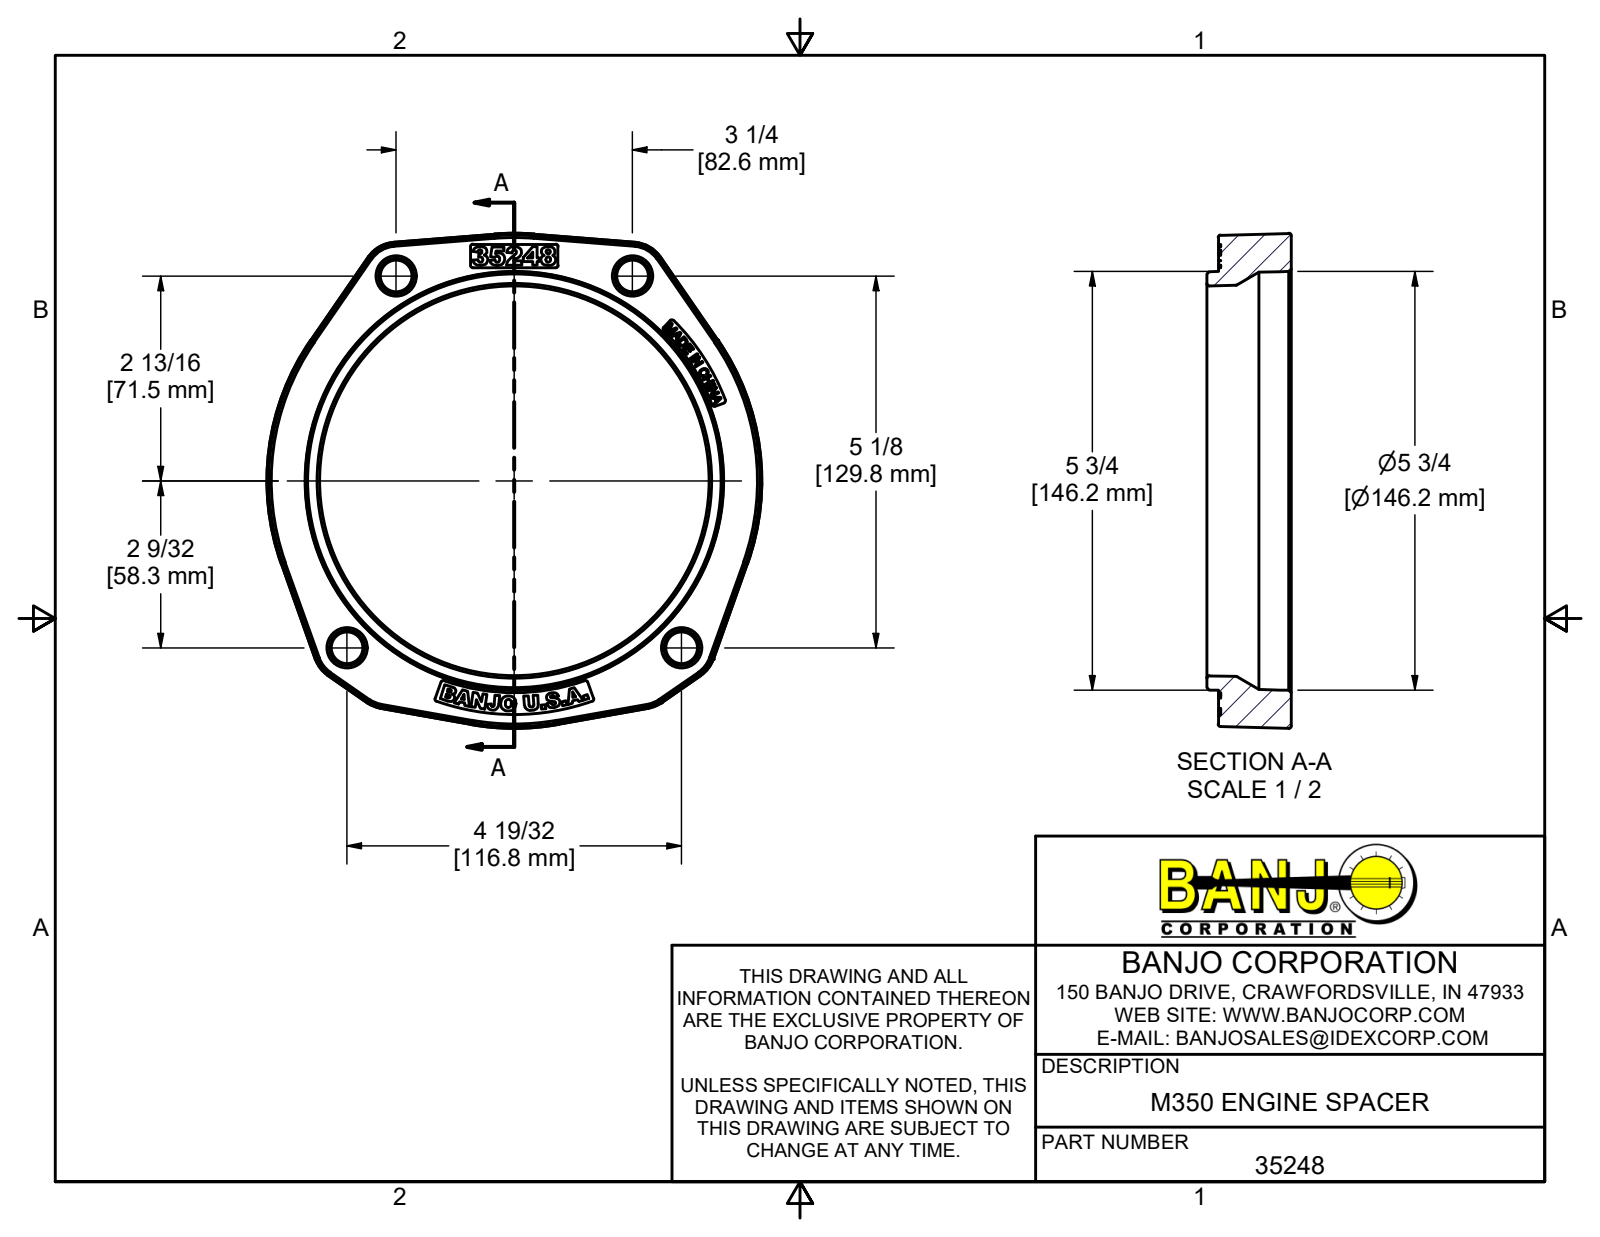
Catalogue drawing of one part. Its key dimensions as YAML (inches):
part_name: "35248"
step_written_by: "Autodesk Inventor 2022 (AUTOMOTIVE_DESIGN)"
units: inches
bodies: {solids: 1, faces: 824, planar: 296, cylindrical: 106, other: 422}
overall_size: [6.801, 6.801, 1.157]
volume: 10.02
surface_area: 106.3
partial_cylinders:
  - {radius: 0.031, count: 86}
  - {radius: 2.91, count: 1}
  - {radius: 3.105, count: 1}
  - {radius: 3.21, count: 1}
face_to_face_distances: [1, 0.15, 1.157, 0.157, 0.15, 0.15, 0.85, 0.307, 0.12, 0.187]
